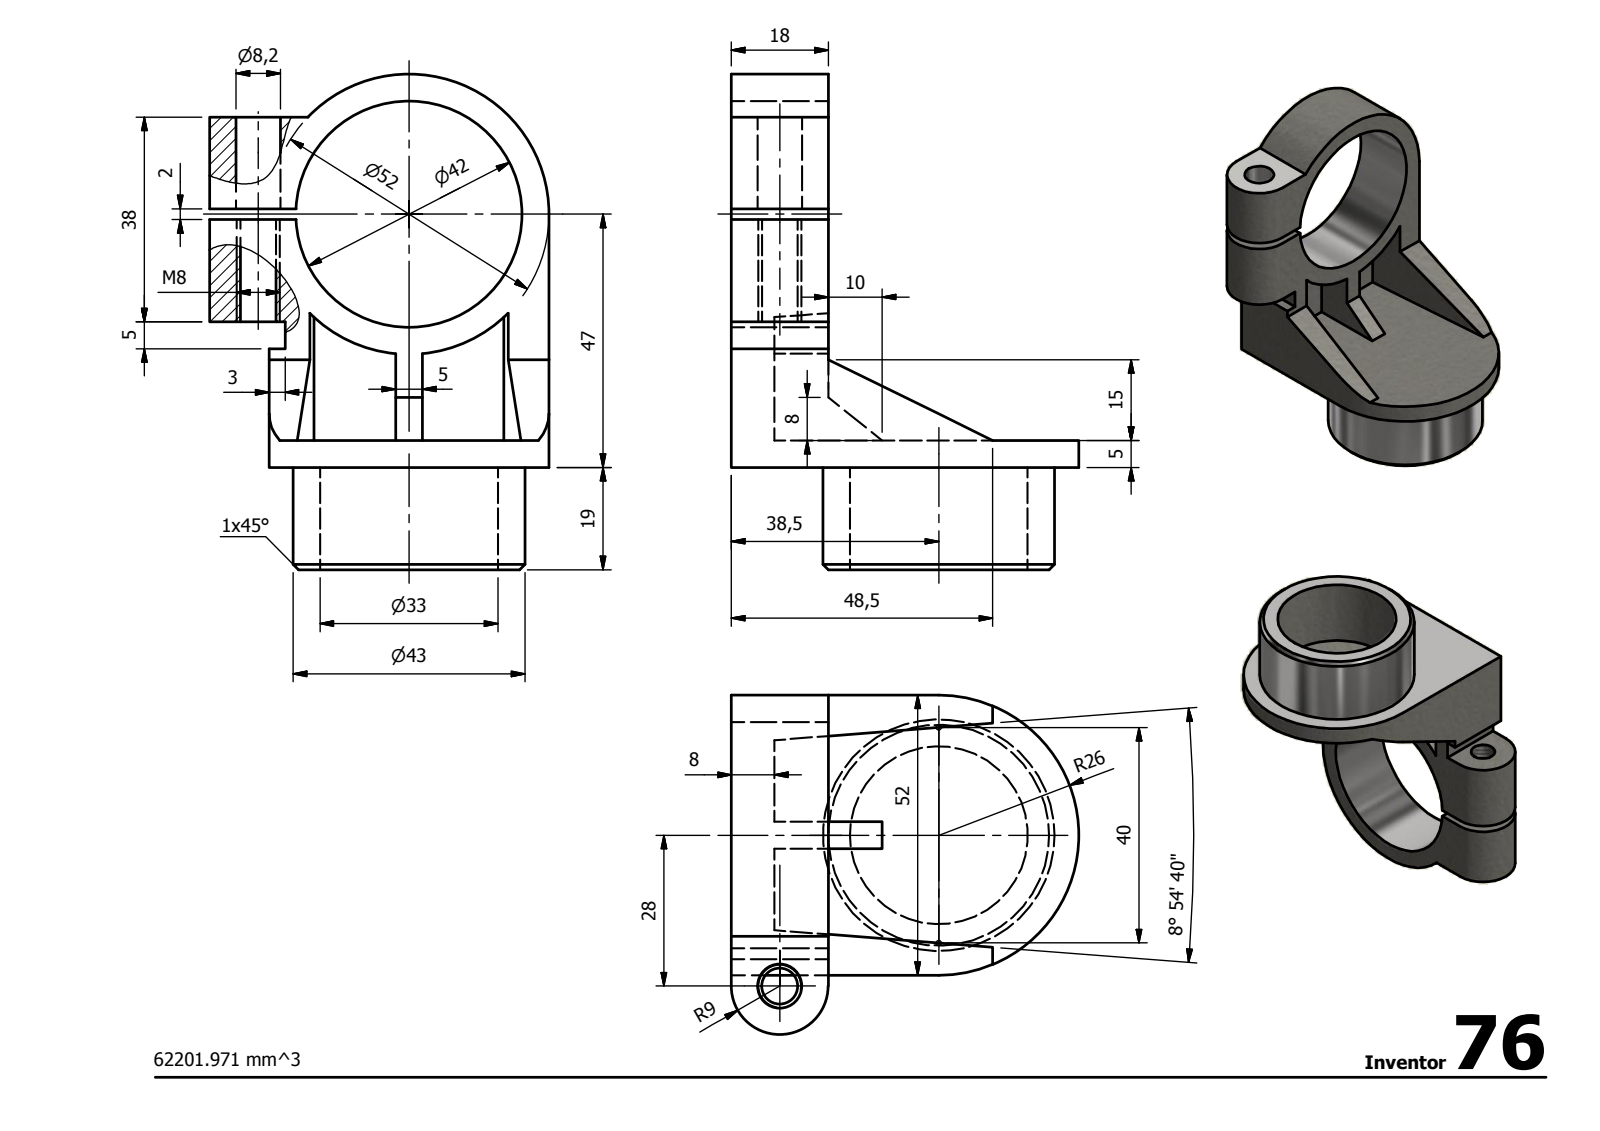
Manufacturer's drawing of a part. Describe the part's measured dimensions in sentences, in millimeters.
Its 3-D file was written by "Autodesk Inventor 2014 (AUTOMOTIVE_DESIGN)". It is 1 solid with 35 faces: 23 planar, 11 cylindrical and 1 other. Overall it measures 92 by 64.5 by 63 millimeters. Its volume is 62 202 cubic millimeters and its surface area 24 148 square millimeters. Round holes: 1 of diameter 6.65, 1 of diameter 8.2, 1 of diameter 33, 1 of diameter 42. Round bosses or shafts: 1 of diameter 43. Partial cylindrical surfaces (rounded edges, fillets, slot ends): 2 of radius 26, 1 of radius 9. The main face-to-face distances are 5, 18, 19, 52, 8, 10, 24, 65, 23.5, 28.5. The hole center spacings are 40.67.
